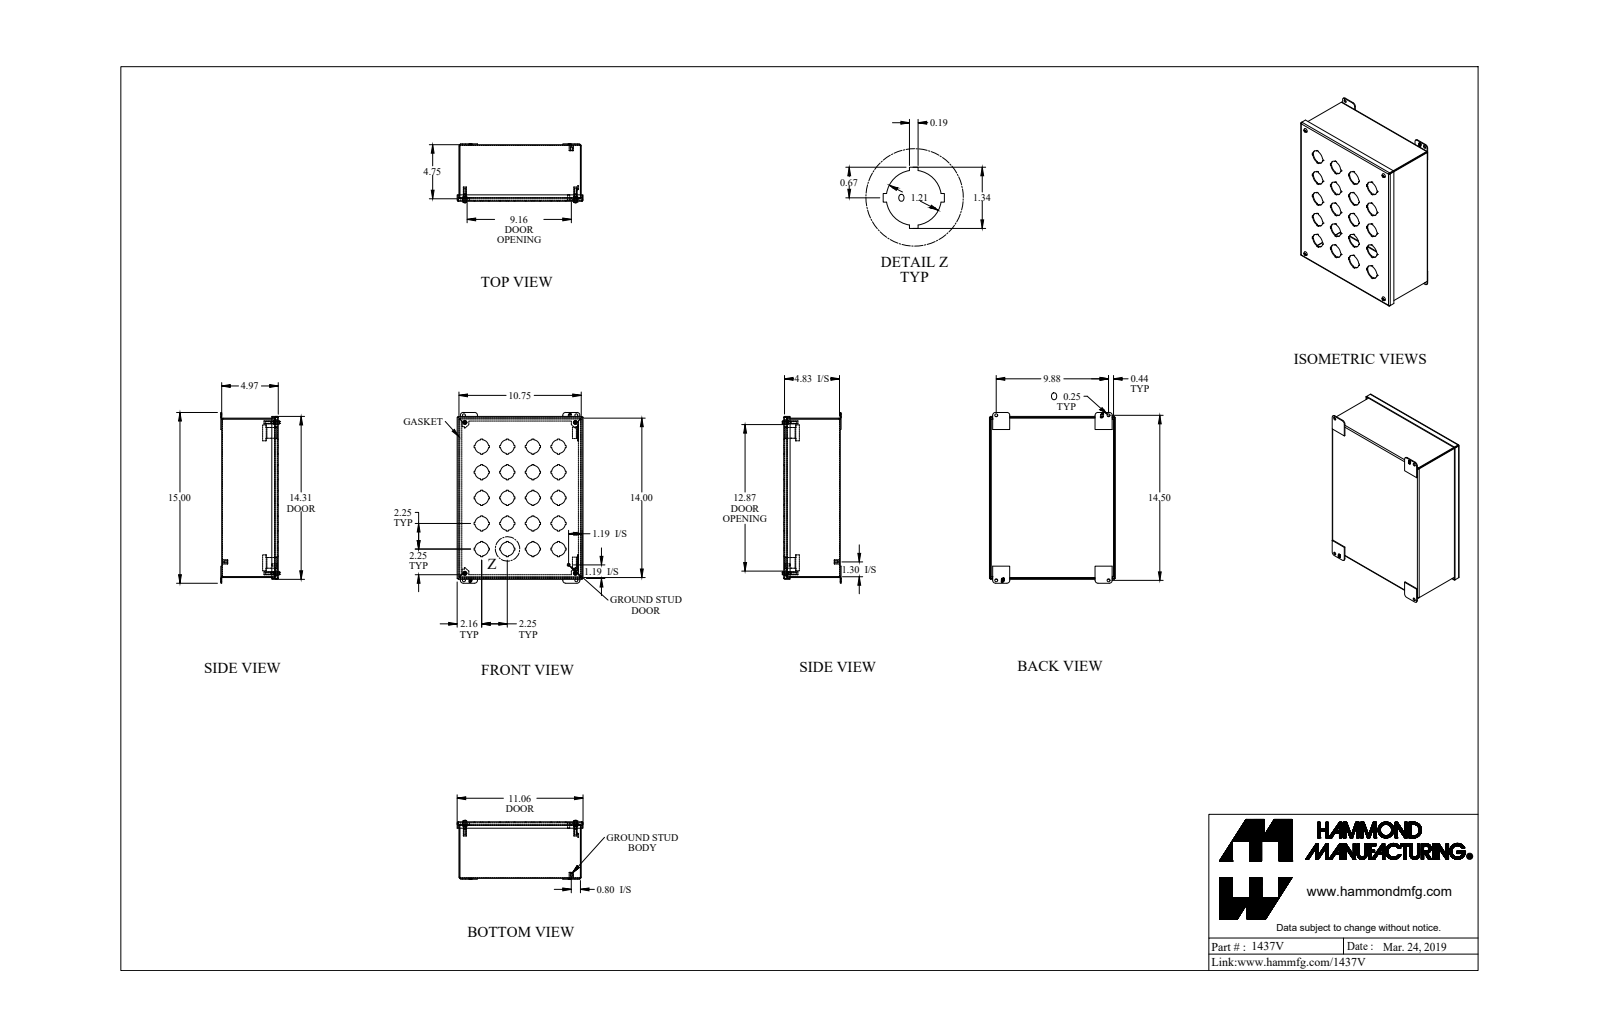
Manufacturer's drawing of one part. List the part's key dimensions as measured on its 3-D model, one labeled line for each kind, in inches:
Part name (STEP PRODUCT): 1437V_Default
STEP written by: SolidWorks 2019 (CONFIG_CONTROL_DESIGN)
Units: inches
Bodies: 23 solids, 1035 faces (739 planar, 240 cylindrical, 56 other)
Overall size (bounding box): 15 × 11.062 × 5.171
Volume: 44.93 in³ · Surface area: 1 205 in²
Round holes (diameter × count): ⌀1.21 ×20, ⌀0.25 ×8, ⌀0.159 ×4, ⌀0.406 ×4, ⌀0.156 ×1
Round bosses / shafts (diameter × count): ⌀0.39 ×4, ⌀0.275 ×4, ⌀0.19 ×4, ⌀0.148 ×4, ⌀0.375 ×1, ⌀0.25 ×1, ⌀0.188 ×1
Partial cylindrical surfaces — rounded edges, fillets, slot ends (radius × count): R0.036 ×12, R0.108 ×12, R0.25 ×8, R0.029 ×4, R0.086 ×4, R0.16 ×4, R0.171 ×4, R0.125 ×2
Main face-to-face distances: 0.072, 4.9, 4.828, 4.972, 10.678, 13.928, 10.75, 10.606, 14, 13.856
Hole centre spacings: 2.25, 5.031, 3.182, 4.5, 7.115, 0.63, 6.364, 6.75
